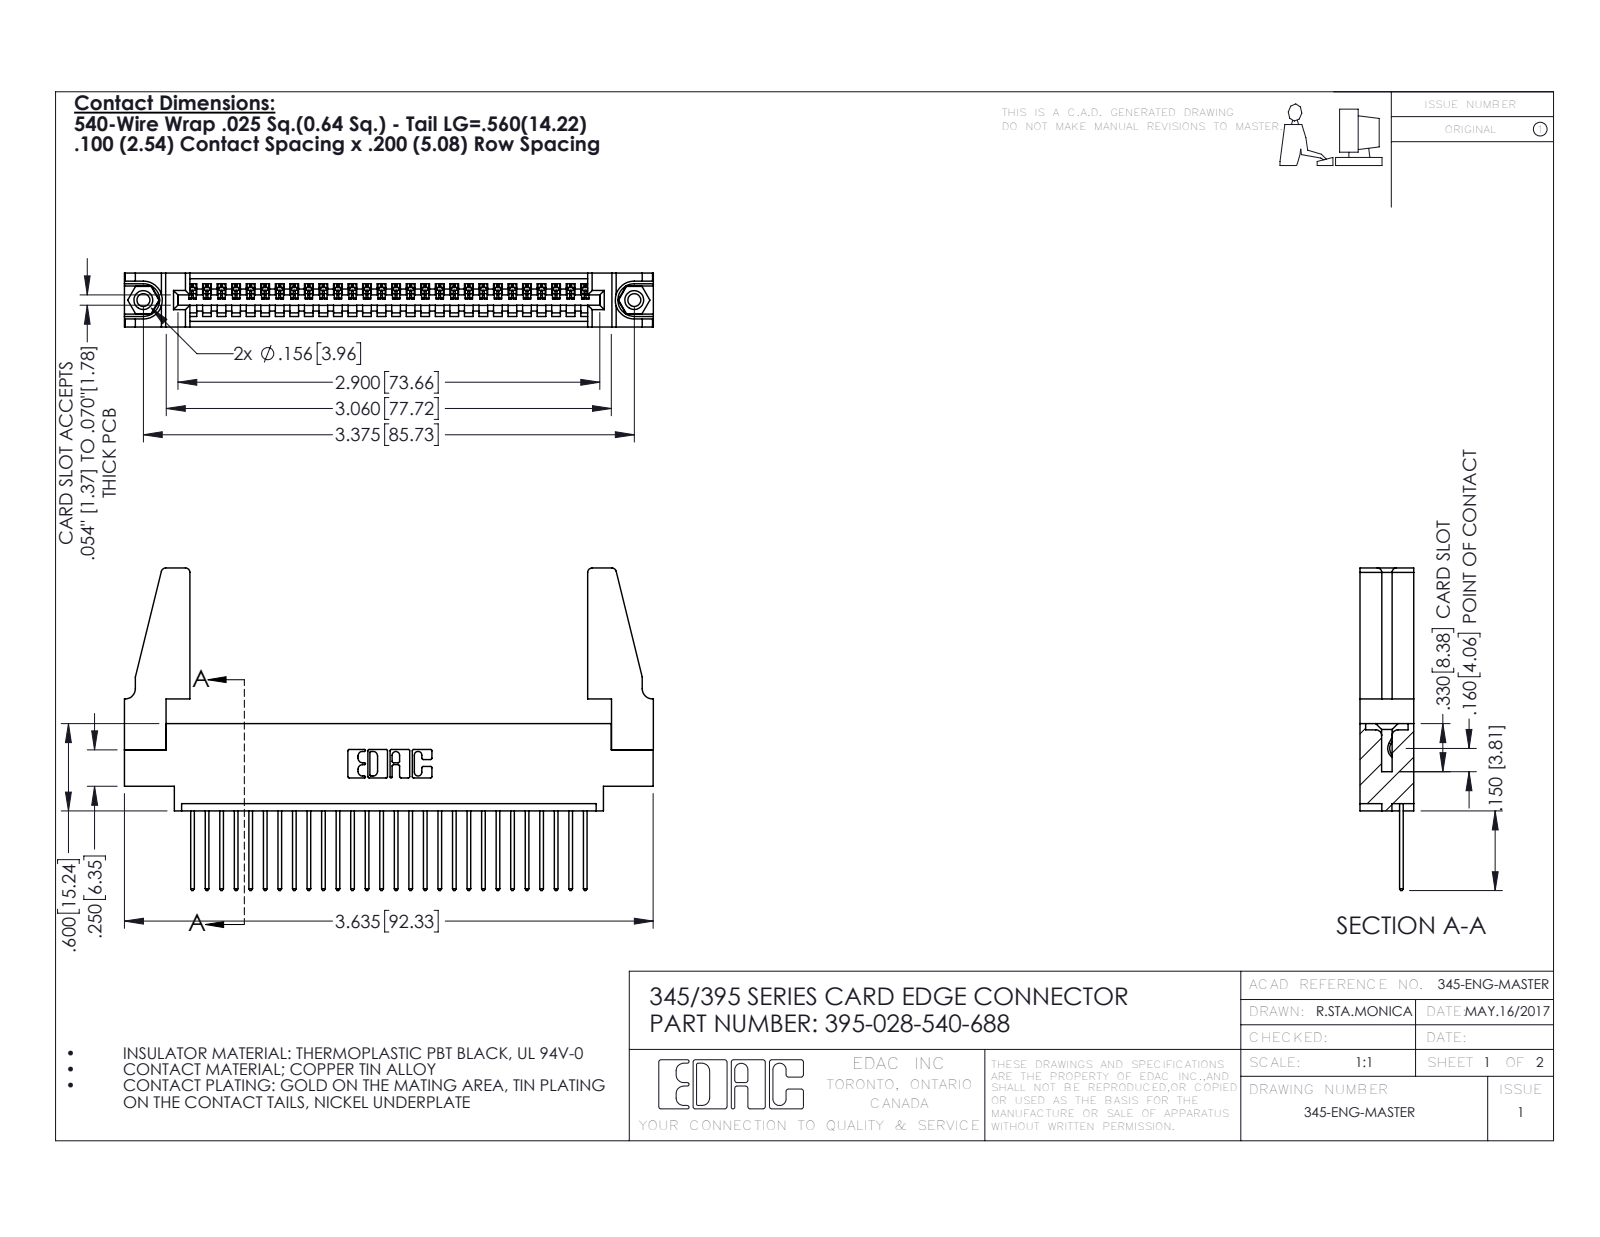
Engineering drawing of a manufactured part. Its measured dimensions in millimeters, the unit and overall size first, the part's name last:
Units: millimetres
Overall size (bounding box): 92.4 × 56.3 × 9.4
Round holes (diameter × count): ⌀2.3 ×2, ⌀3.2 ×2, ⌀4 ×2, ⌀1.6 ×1
Round bosses / shafts (diameter × count): ⌀3.9 ×2
Partial cylindrical surfaces — rounded edges, fillets, slot ends (radius × count): R0.2 ×56, R0.3 ×56, R0.3 ×22, R0.8 ×8, R0.2 ×6, R0.8 ×6, R0.7 ×3, R0.8 ×2
Main face-to-face distances: 1.8, 9.4, 7.6, 2.5, 6.9, 0.6, 5.1, 5.7, 4.4, 3.8
Hole centre spacings: 6.9, 79.8, 85.7
Volume: 11 800 mm³ · Surface area: 14 740 mm²
Bodies: 33 solids, 1878 faces (1276 planar, 586 cylindrical, 16 other)
Part name (STEP PRODUCT): 345-250-001_345-250-001-102; 345-292-001_345-293-140; 345-220-078_345-220-088; 395-028-540-688 (+1 more)
STEP written by: SolidWorks 2016 (CONFIG_CONTROL_DESIGN)
